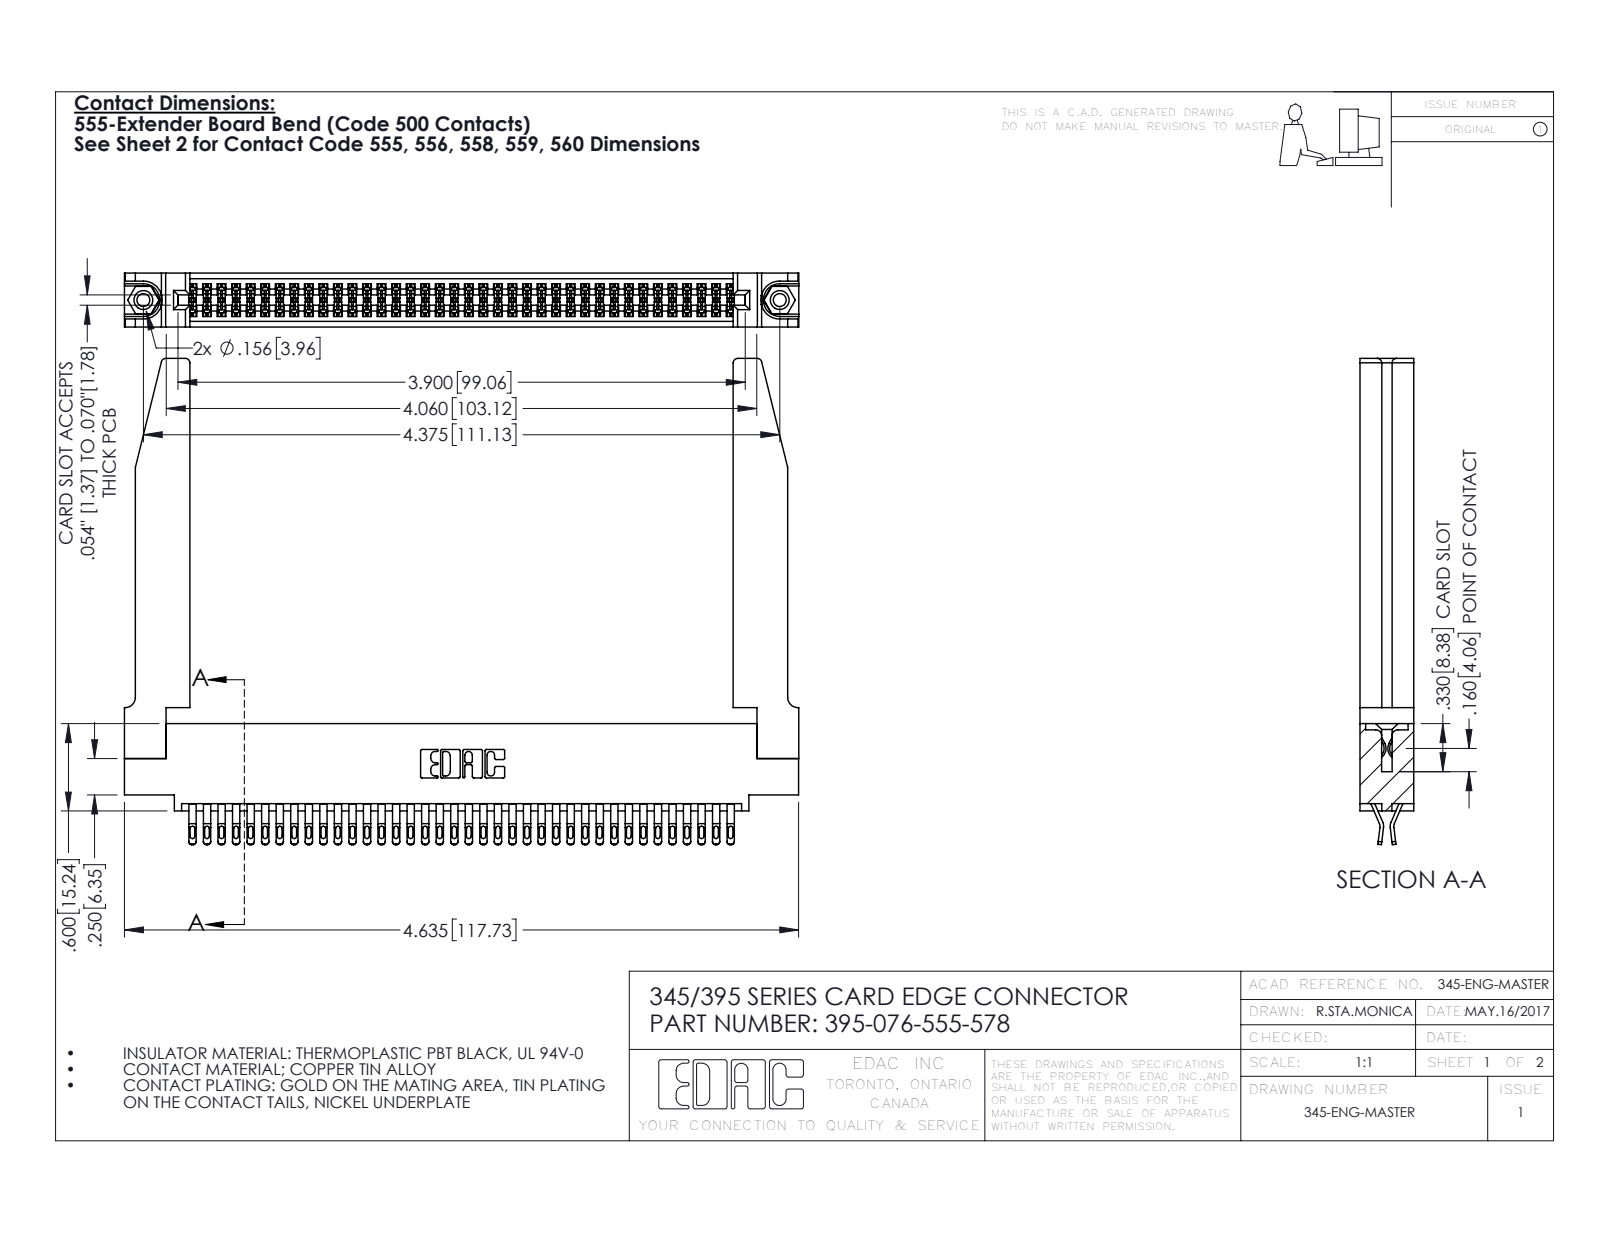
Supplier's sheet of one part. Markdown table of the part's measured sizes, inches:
| quantity | value |
| --- | --- |
| part name | 345 Part_0.110 Offset - 0.156 Dia-TH; 345-220-078_345-220-078; 395-076-555-578; 345-292-001_555 Tail (+1 more) |
| STEP written by | SolidWorks 2016 (CONFIG_CONTROL_DESIGN) |
| units | inches |
| bodies | 81 solids, 4620 faces (2582 planar, 1986 cylindrical, 52 other) |
| overall size | 4.636 × 3.342 × 0.37 |
| volume | 1.179 in³ |
| surface area | 38.27 in² |
| round holes (diameter × count) | 0.089 × 2, 0.125 × 2, 0.156 × 2, 0.064 × 1 |
| round bosses / shafts (diameter × count) | 0.155 × 2 |
| partial cylindrical surfaces (radius × count) | 0.016 × 190, 0.02 × 152, 0.006 × 114, 0.01 × 22, 0.03 × 8, 0.007 × 6, 0.031 × 6, 0.026 × 3 |
| main face-to-face distances | 0.37, 0.072, 0.298, 0.025, 0.2, 0.098, 0.272, 0.225, 0.148, 0.15 |
| hole center spacings | 0.27, 4.139, 4.375 |
